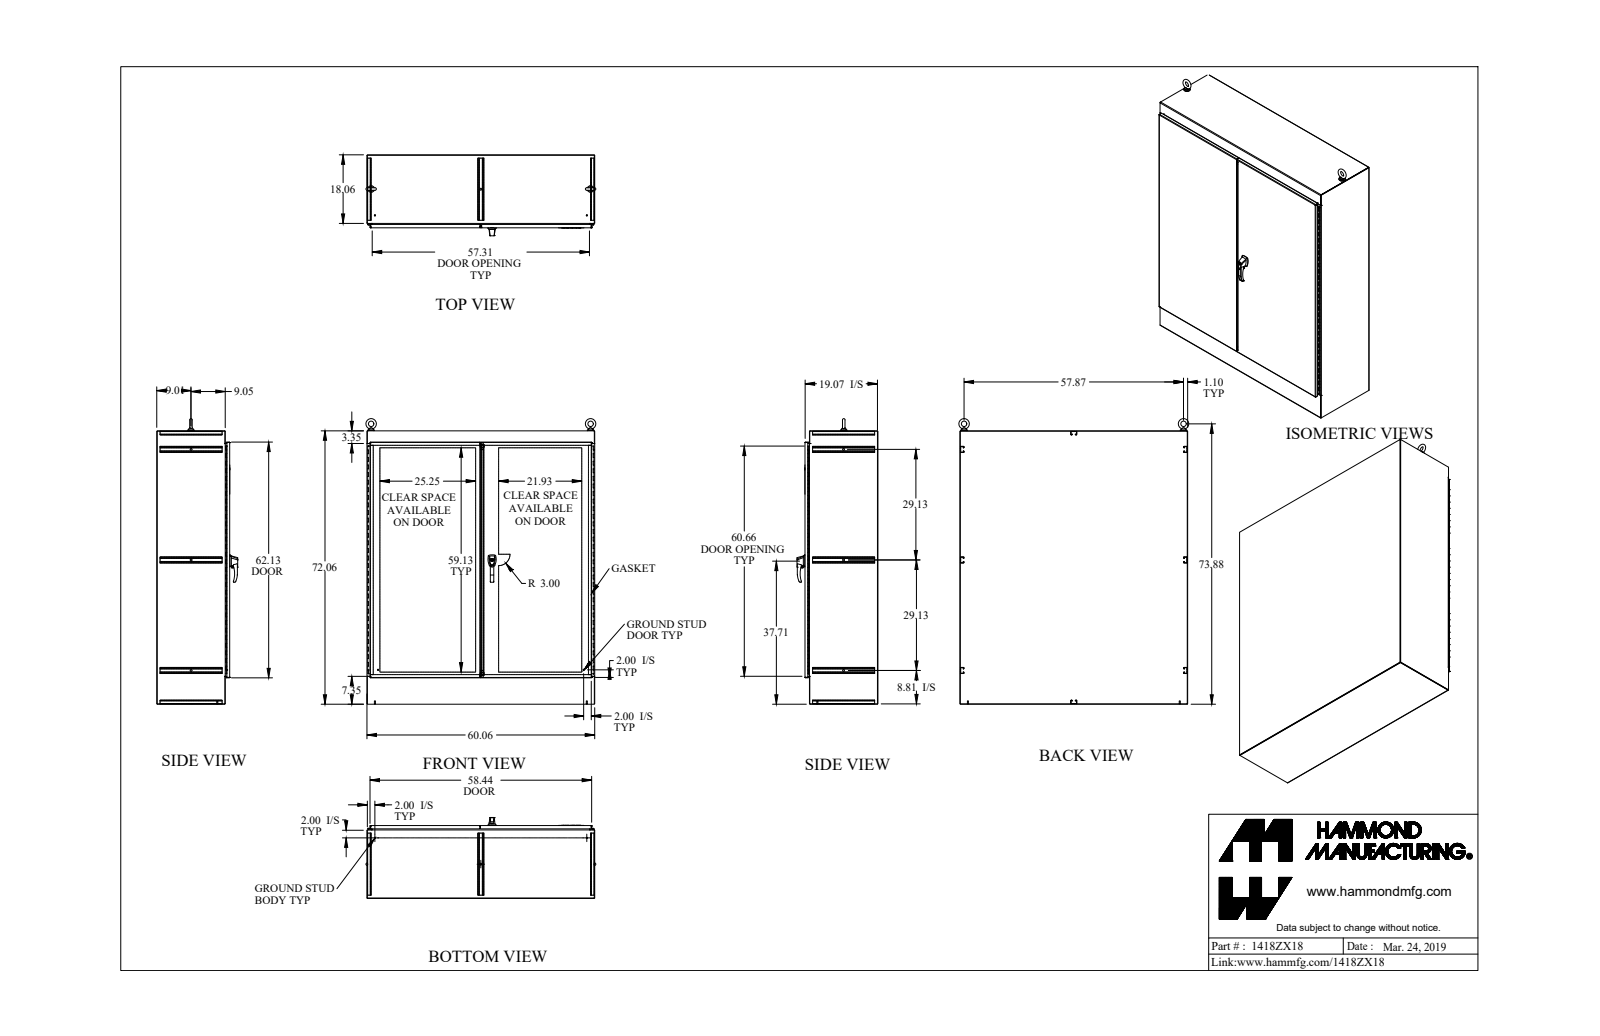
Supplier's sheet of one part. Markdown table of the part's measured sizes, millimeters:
| quantity | value |
| --- | --- |
| part name | 1418ZX18_Default |
| STEP written by | SolidWorks 2019 (CONFIG_CONTROL_DESIGN) |
| units | millimeters |
| bodies | 71 solids, 2583 faces (1198 planar, 1220 cylindrical, 165 other) |
| overall size | 1923.1 × 1552.4 × 542 |
| volume | 27 220 000 mm³ |
| surface area | 20 710 000 mm² |
| round holes (diameter × count) | 7.7 × 20, 12.7 × 4, 2.8 × 2, 6.4 × 2, 6.5 × 2, 7.1 × 2, 7.1 × 2, 8 × 2, 9.9 × 2, 10.5 × 2, 13.4 × 2, 15.9 × 2 |
| round bosses / shafts (diameter × count) | 7.1 × 6, 6.4 × 4, 44.5 × 2, 38.1 × 2, 31.8 × 2, 25.4 × 2, 19.1 × 2, 18.7 × 2 |
| partial cylindrical surfaces (radius × count) | 1.1 × 54, 3.5 × 48, 3.2 × 22, 1.2 × 20, 3.6 × 20, 0.5 × 16, 1.5 × 10, 1.3 × 8 |
| main face-to-face distances | 2.4, 3.2, 482.7, 485.8, 485.1, 488.2, 1523.1, 1827.9, 29.5, 1520.7 |
| hole center spacings | 152.4, 1489.4, 304.8, 1512.6, 457.2, 1550.5, 609.6, 1602.1 |
